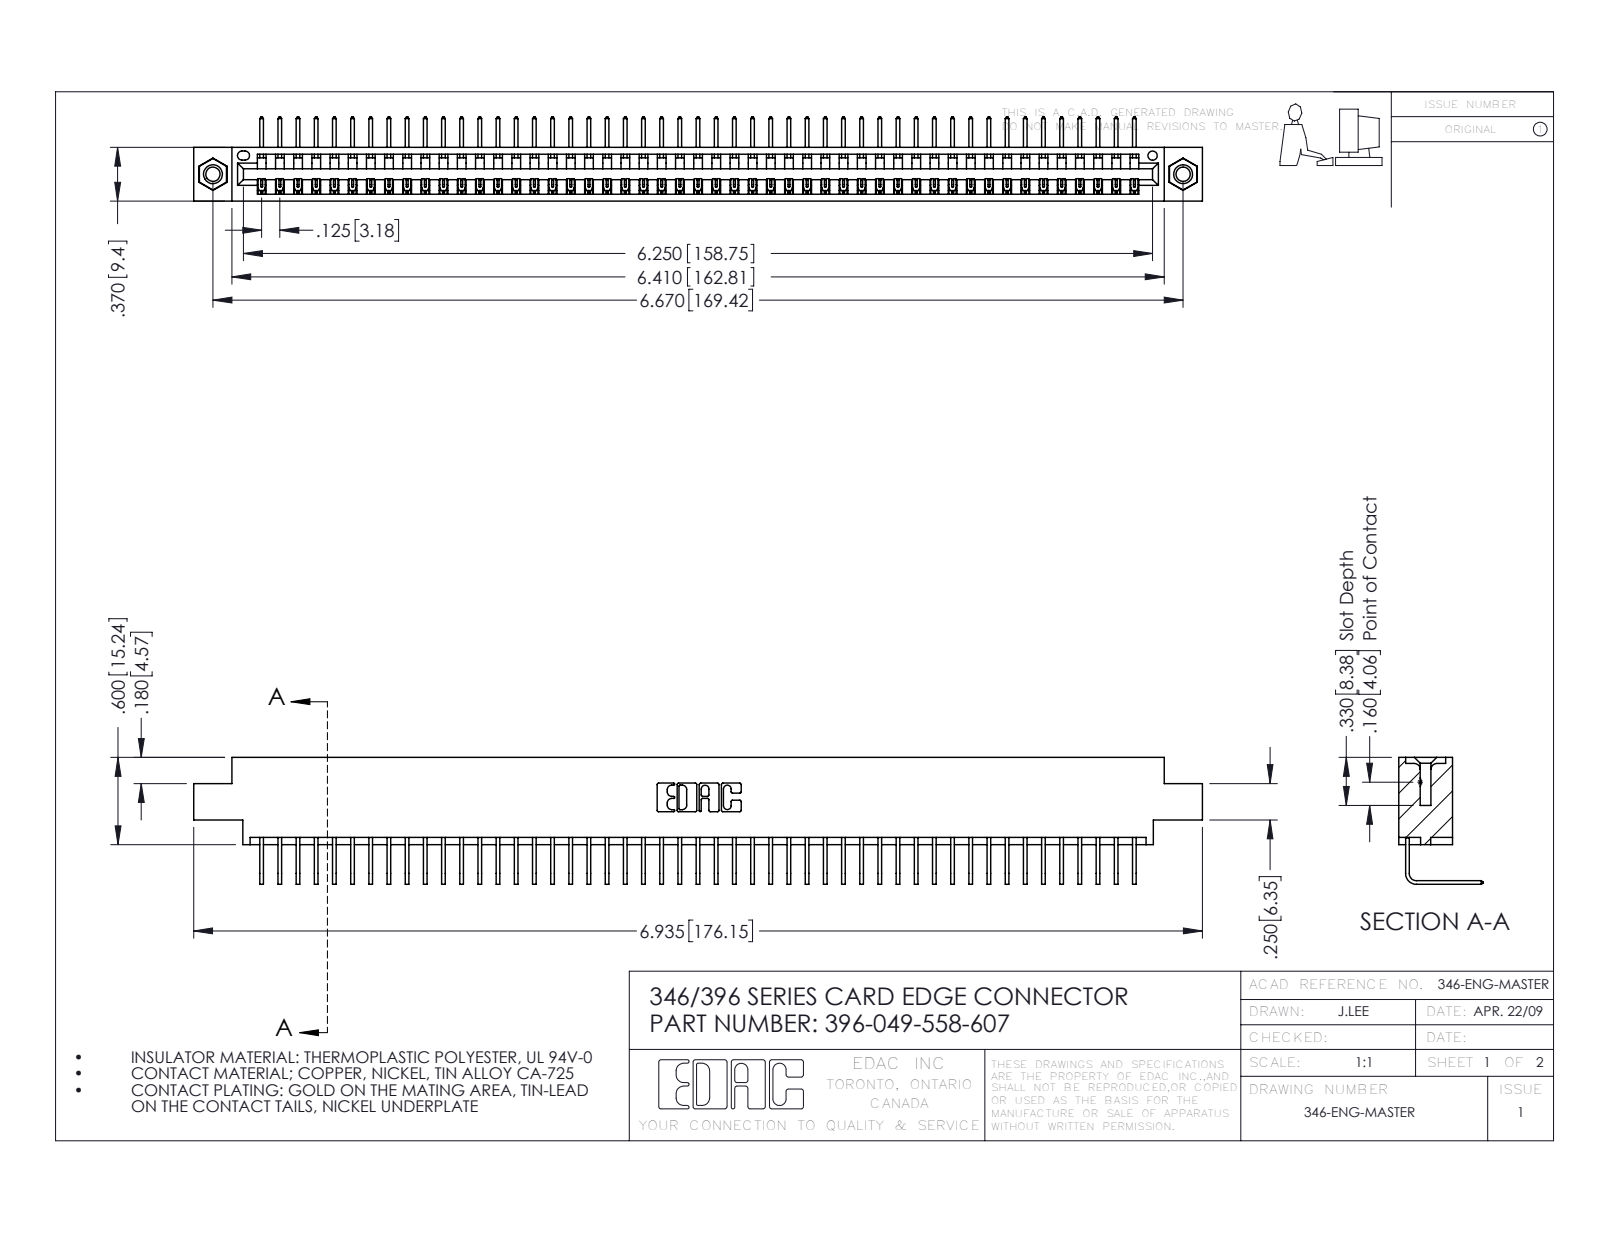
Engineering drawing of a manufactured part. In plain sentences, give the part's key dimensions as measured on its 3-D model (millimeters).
The part is named "396-049-558-607; 346 Part_0.170 Offset - 0.156 Dia-TI; 345-250-001_345-250-005-103; 345-292-001_558 Tail - 2". Its 3-D file was written by "SolidWorks 2016 (CONFIG_CONTROL_DESIGN)". It is 52 solids with 3126 faces: 2170 planar, 940 cylindrical and 16 other. Overall it measures 176.1 by 22.2 by 14.7 millimeters. Its volume is 16 910 cubic millimeters and its surface area 22 370 square millimeters. Round holes: 2 of diameter 2.5, 2 of diameter 3.2, 2 of diameter 4, 1 of diameter 1.6. Round bosses or shafts: 2 of diameter 3.9. Partial cylindrical surfaces (rounded edges, fillets, slot ends): 98 of radius 0.2, 22 of radius 0.3, 6 of radius 0.2, 6 of radius 0.8, 3 of radius 0.7, 2 of radius 0.8, 2 of radius 1, 1 of radius 0.4. The main face-to-face distances are 8.2, 1.2, 9.4, 6.4, 7.6, 0.6, 1.8, 5.6, 3.8, 2.5. The hole center spacings are 6.2, 164.1, 169.4.
